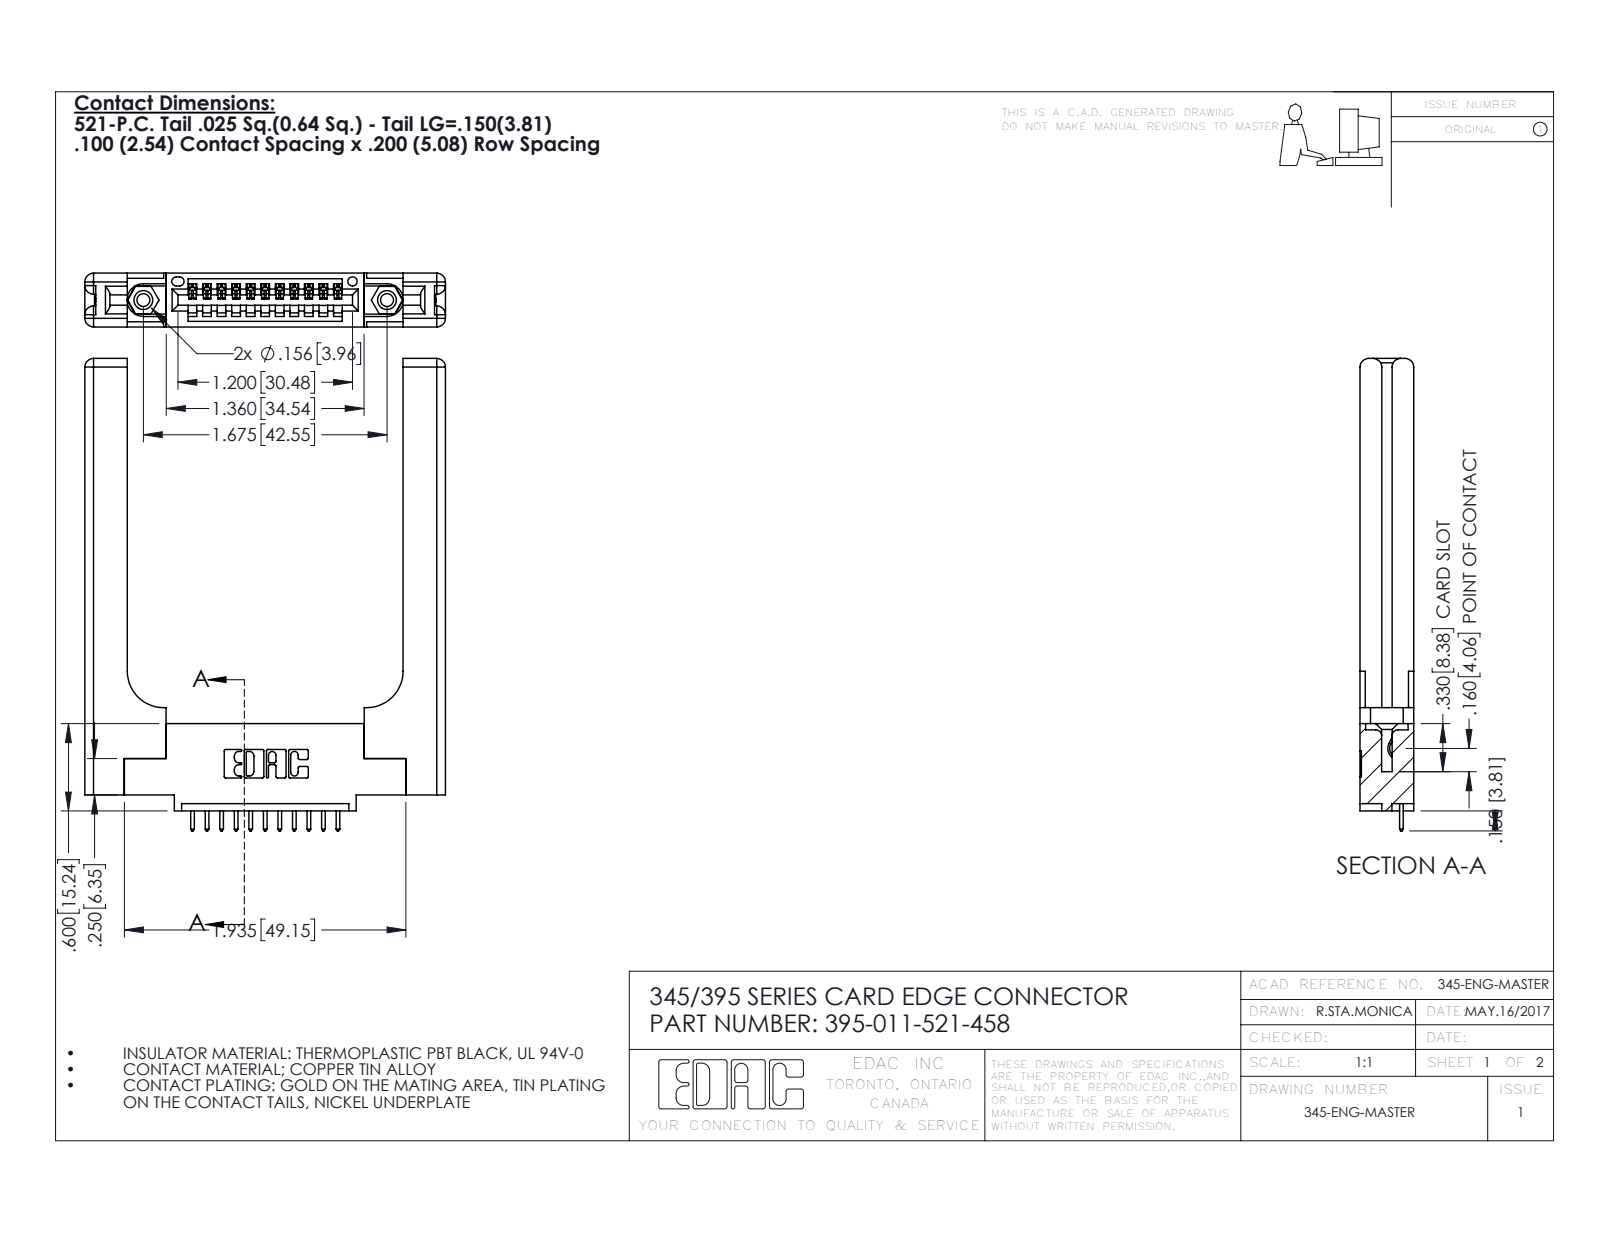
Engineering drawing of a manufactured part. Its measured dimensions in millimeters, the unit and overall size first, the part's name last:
Units: millimetres
Overall size (bounding box): 82.5 × 63 × 9.4
Round holes (diameter × count): ⌀2.3 ×2, ⌀3.2 ×2, ⌀4 ×2, ⌀1.6 ×1
Round bosses / shafts (diameter × count): ⌀3.9 ×2
Partial cylindrical surfaces — rounded edges, fillets, slot ends (radius × count): R0.2 ×22, R0.3 ×22, R0.3 ×22, R1.5 ×16, R0.2 ×6, R0.8 ×6, R0.7 ×3, R0.8 ×2
Main face-to-face distances: 9.4, 1.8, 3.8, 5.6, 3.8, 2, 7.6, 48.2, 1.8, 5.1
Hole centre spacings: 6.9, 36.7, 42.5
Volume: 14 100 mm³ · Surface area: 12 320 mm²
Bodies: 16 solids, 1024 faces (672 planar, 292 cylindrical, 60 other)
Part name (STEP PRODUCT): 345 Part_0.110 Offset - 0.156 Dia-TH; 345-292-001_345-293-121; 345-220-058_345-220-058; 395-011-521-458 (+1 more)
STEP written by: SolidWorks 2016 (CONFIG_CONTROL_DESIGN)
